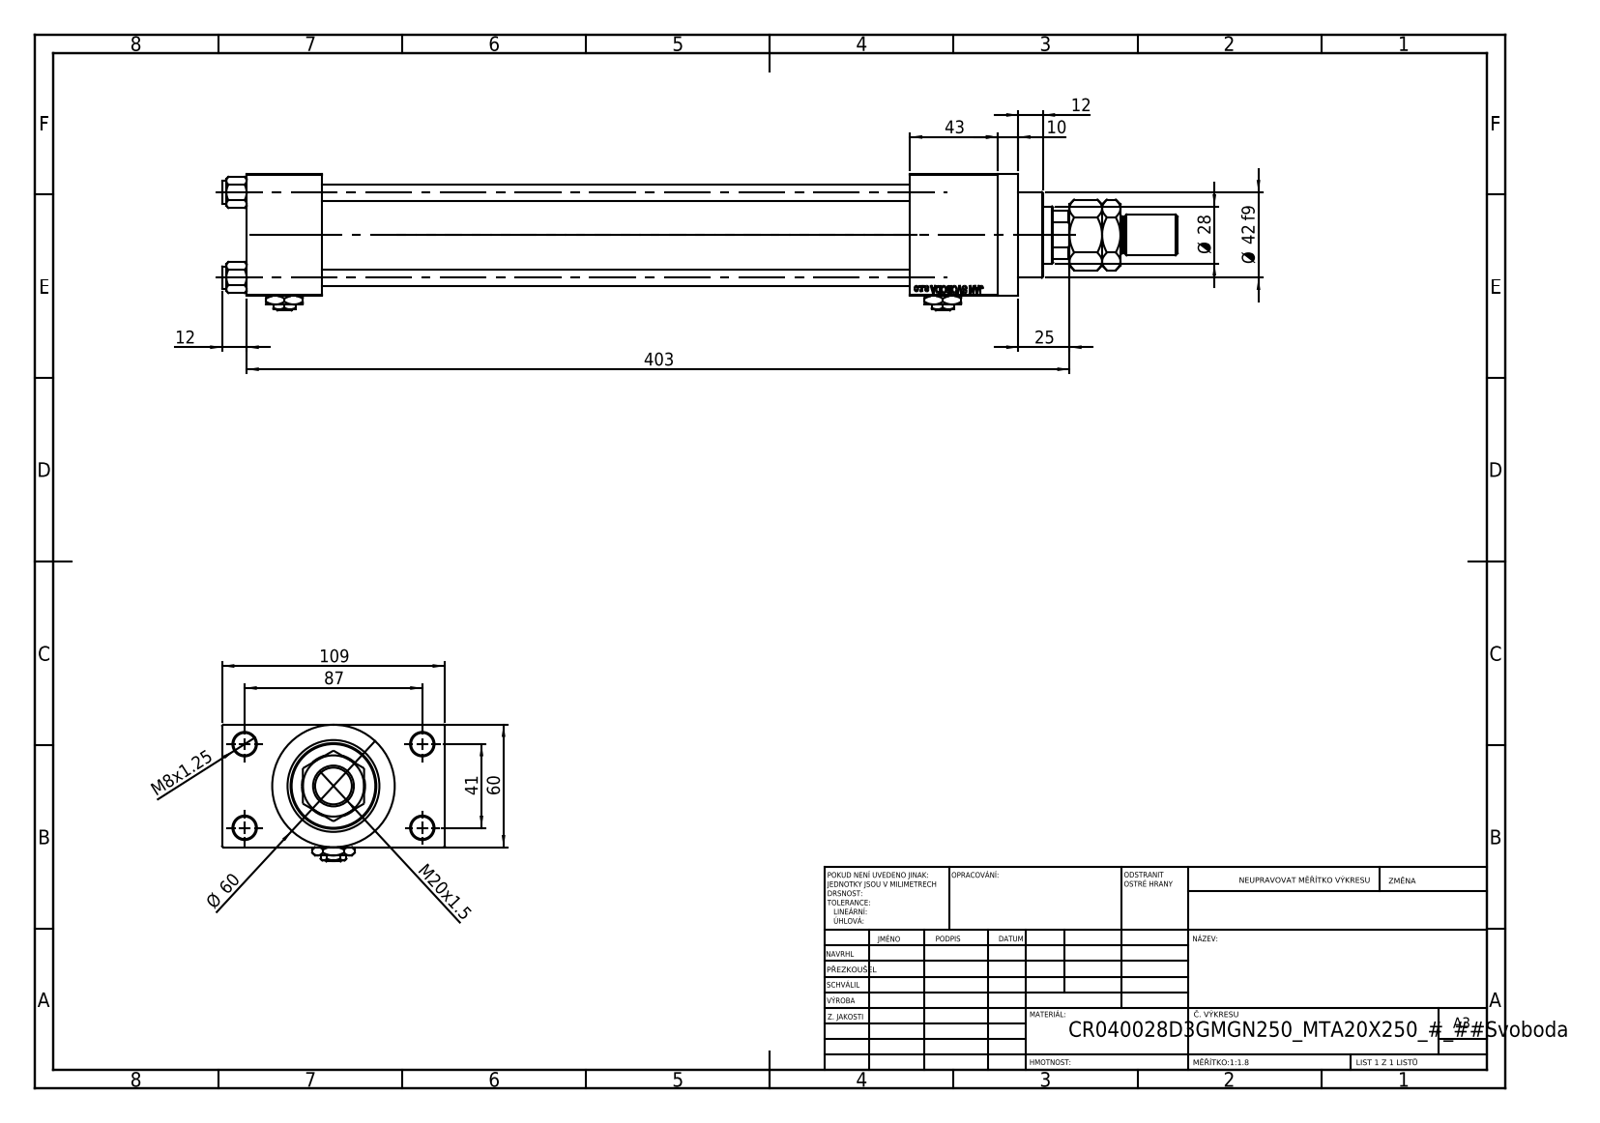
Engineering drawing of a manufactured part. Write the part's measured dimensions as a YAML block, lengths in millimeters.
part_name: "Zatka_pro_OIL_PORT; V215CR_D_Body; V215CR_VCP_D; V215_VC_A (+3 more)"
step_written_by: "SolidWorks 2019 (CONFIG_CONTROL_DESIGN)"
units: millimeters
bodies: {solids: 14, faces: 1254, planar: 561, cylindrical: 103, other: 590}
overall_size: [468, 109, 67]
volume: 836004
surface_area: 243016
round_holes:
  - {diameter: 8, count: 4}
  - {diameter: 11, count: 4}
  - {diameter: 16.66, count: 4}
  - {diameter: 24, count: 4}
  - {diameter: 7, count: 3}
  - {diameter: 18.5, count: 1}
  - {diameter: 28, count: 1}
  - {diameter: 31, count: 1}
  - {diameter: 40, count: 1}
  - {diameter: 45, count: 1}
round_bosses_or_shafts:
  - {diameter: 11, count: 4}
  - {diameter: 60, count: 1}
  - {diameter: 46, count: 1}
  - {diameter: 42, count: 1}
  - {diameter: 20, count: 1}
  - {diameter: 18, count: 1}
partial_cylinders:
  - {radius: 13.5, count: 1}
face_to_face_distances: [60, 24.5, 288, 84.5, 37, 325, 368, 331, 43, 109]
hole_center_spacings: [22.65, 29.49, 41.7, 47.15, 48.09, 64.35, 76.49, 41]
